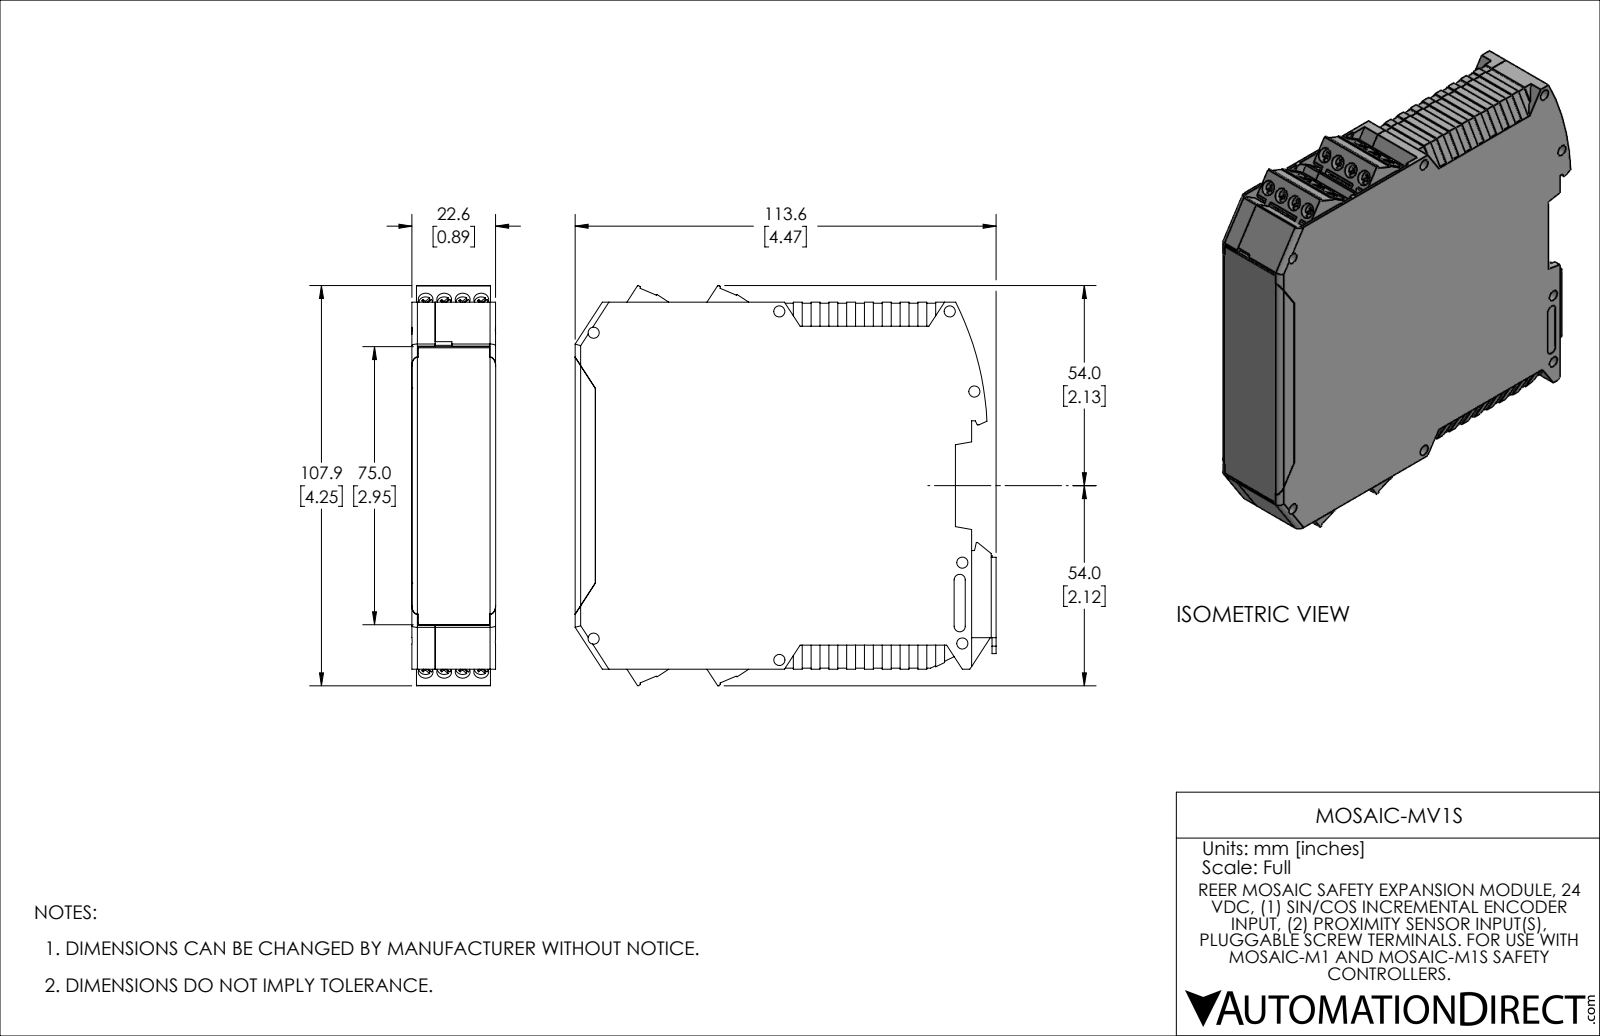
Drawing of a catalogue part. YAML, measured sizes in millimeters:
part_name: "MOSAIC-MV1S"
step_written_by: "SolidWorks 2021 (AUTOMOTIVE_DESIGN)"
units: millimeters
bodies: {solids: 9, faces: 1954, planar: 1569, cylindrical: 379, other: 6}
overall_size: [113.6, 108, 22.6]
volume: 57090
surface_area: 75810
round_holes:
  - {diameter: 1.4, count: 18}
  - {diameter: 2.8, count: 16}
  - {diameter: 4, count: 16}
  - {diameter: 3, count: 14}
  - {diameter: 1.6, count: 1}
round_bosses_or_shafts:
  - {diameter: 3.8, count: 16}
  - {diameter: 4.5, count: 1}
  - {diameter: 2.8, count: 1}
  - {diameter: 1.3, count: 1}
partial_cylinders:
  - {radius: 0.3, count: 33}
  - {radius: 2.9, count: 16}
  - {radius: 0.2, count: 12}
  - {radius: 0.8, count: 12}
  - {radius: 1.5, count: 8}
  - {radius: 0.8, count: 6}
  - {radius: 2.5, count: 5}
  - {radius: 0.6, count: 4}
face_to_face_distances: [1.2, 21.4, 22.6, 20.1, 1, 6.3, 1.2, 5.1, 15.1, 16.3]
hole_center_spacings: [5, 10, 15, 12.8, 12.8, 18.8, 18.8, 11.8]
